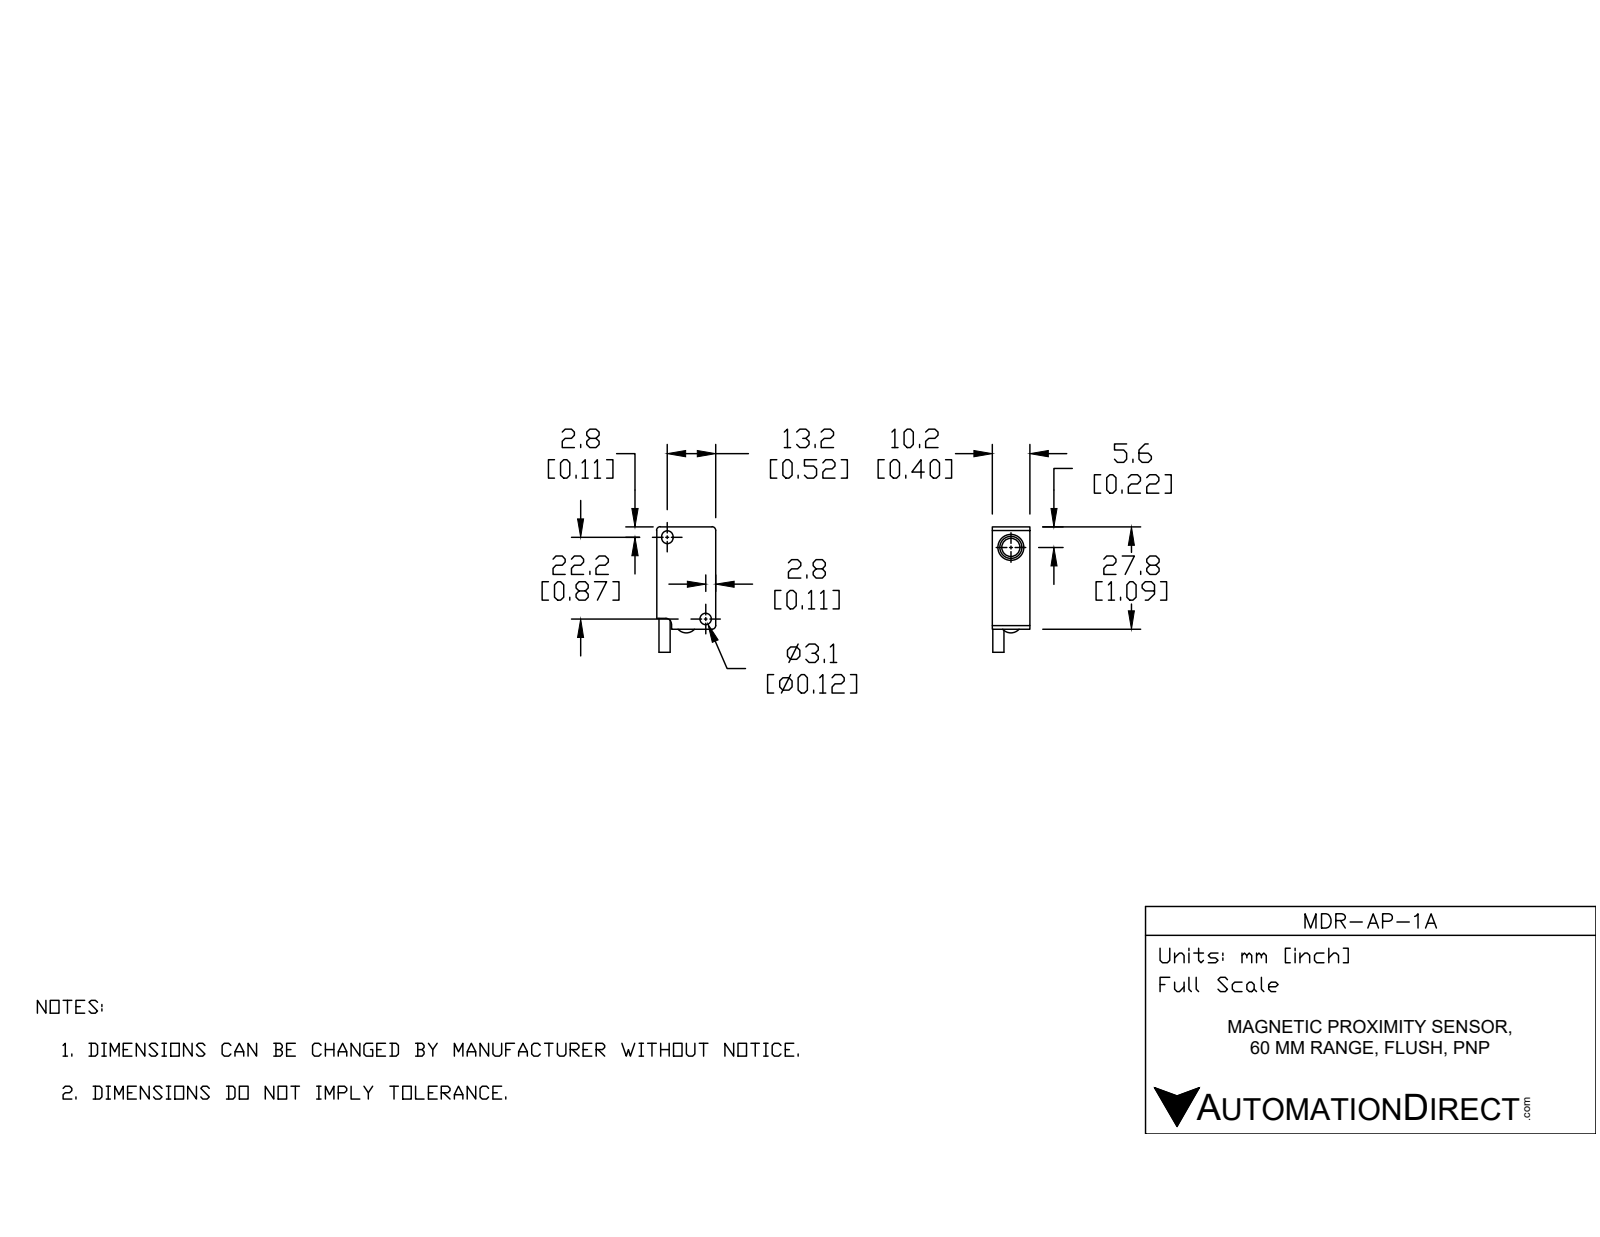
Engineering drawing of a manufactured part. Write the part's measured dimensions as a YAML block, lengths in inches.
part_name: "MDR-AP-1A"
step_written_by: "SolidWorks 2017 (AUTOMOTIVE_DESIGN)"
units: inches
bodies: {solids: 1, faces: 31, planar: 14, cylindrical: 16, other: 1}
overall_size: [1.339, 0.63, 0.402]
volume: 0.263
surface_area: 3.147
round_holes:
  - {diameter: 0.122, count: 1}
  - {diameter: 0.197, count: 1}
  - {diameter: 0.276, count: 1}
round_bosses_or_shafts:
  - {diameter: 0.236, count: 1}
  - {diameter: 0.118, count: 1}
partial_cylinders:
  - {radius: 0.039, count: 3}
  - {radius: 0.061, count: 2}
  - {radius: 0.059, count: 1}
face_to_face_distances: [0.402, 0.63, 1.094, 0.61, 0.02, 0.118, 0.976, 0.157, 0.453, 0.472]
